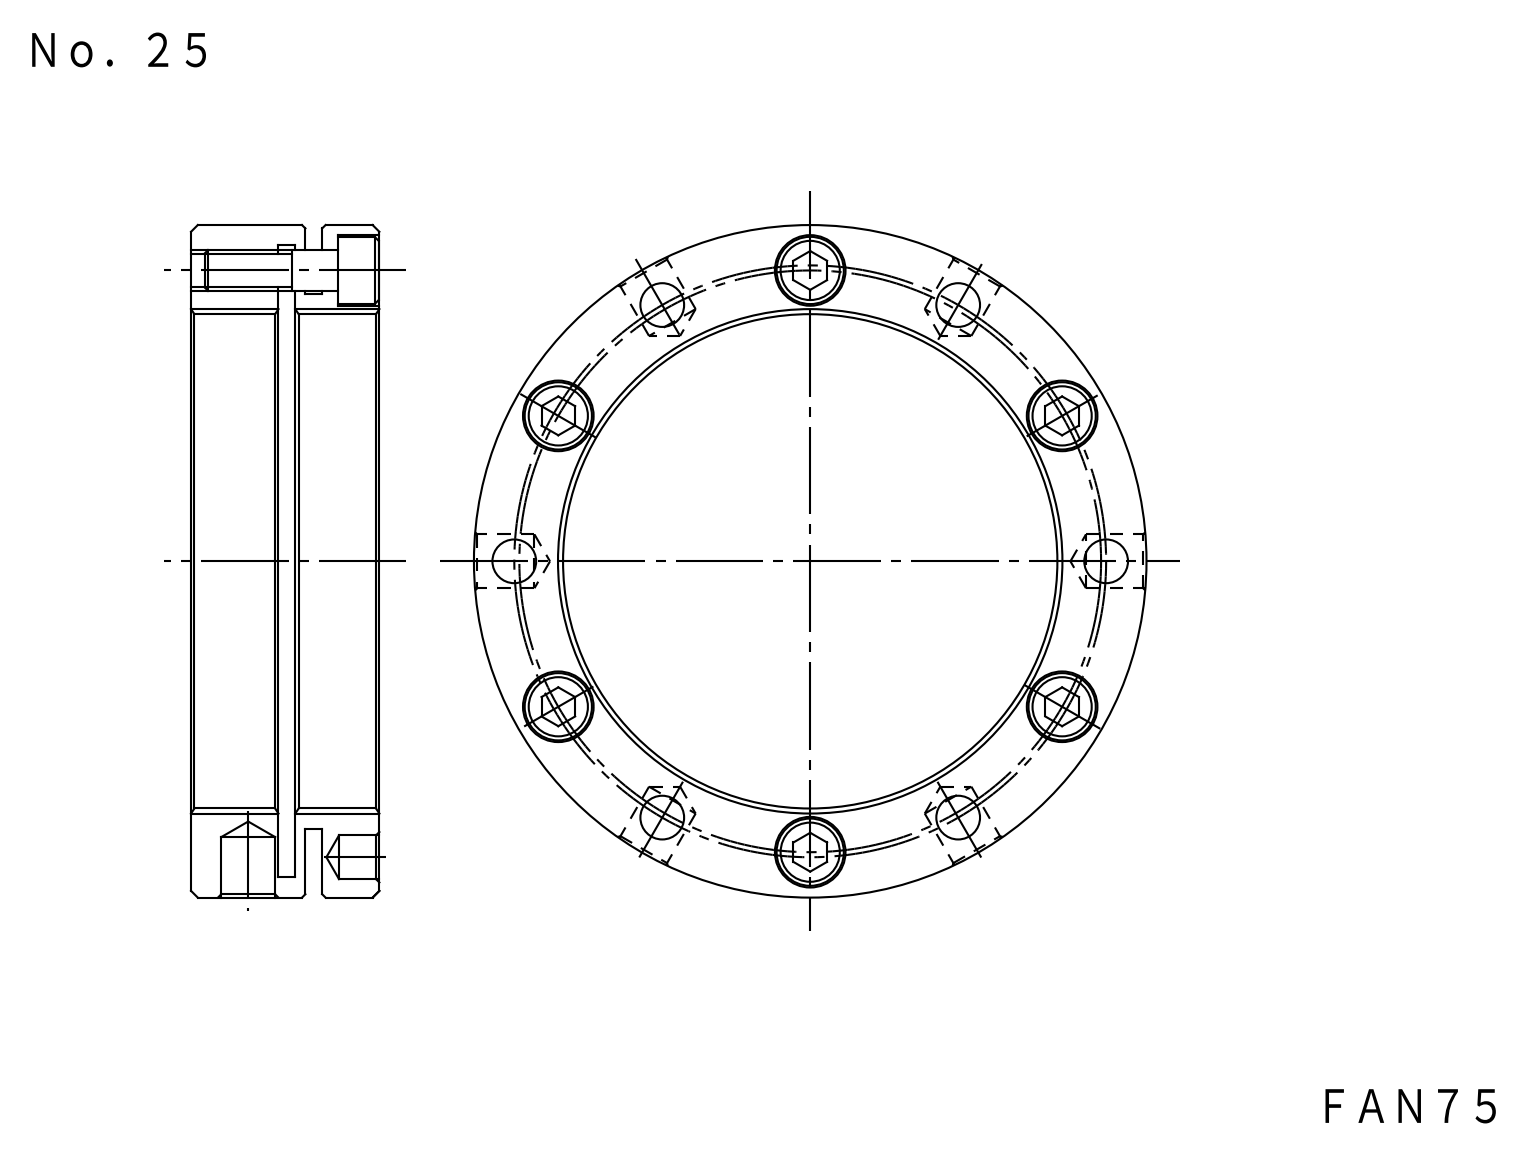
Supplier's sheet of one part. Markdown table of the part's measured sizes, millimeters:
| quantity | value |
| --- | --- |
| part name | FKD FAN75; M6X20_default |
| STEP written by | SolidWorks 2012 (CONFIG_CONTROL_DESIGN) |
| units | millimeters |
| bodies | 7 solids, 204 faces (72 planar, 108 cylindrical, 24 other) |
| overall size | 100 × 100 × 28 |
| volume | 79 495 mm³ |
| surface area | 41 384 mm² |
| round holes (diameter × count) | 6.3 × 6, 6.5 × 6, 10.5 × 6, 4.92 × 3, 4.92 × 3, 8 × 3, 75 × 1, 94 × 1 |
| round bosses / shafts (diameter × count) | 10 × 6, 6 × 6, 100 × 1, 80 × 1 |
| main face-to-face distances | 2.5, 4, 20, 28, 17.5, 10.5, 8, 13.5, 6.5, 14.5 |
| hole center spacings | 22.65, 43.5, 44, 84.52, 61.87, 75.34, 61.88, 76.21 |
